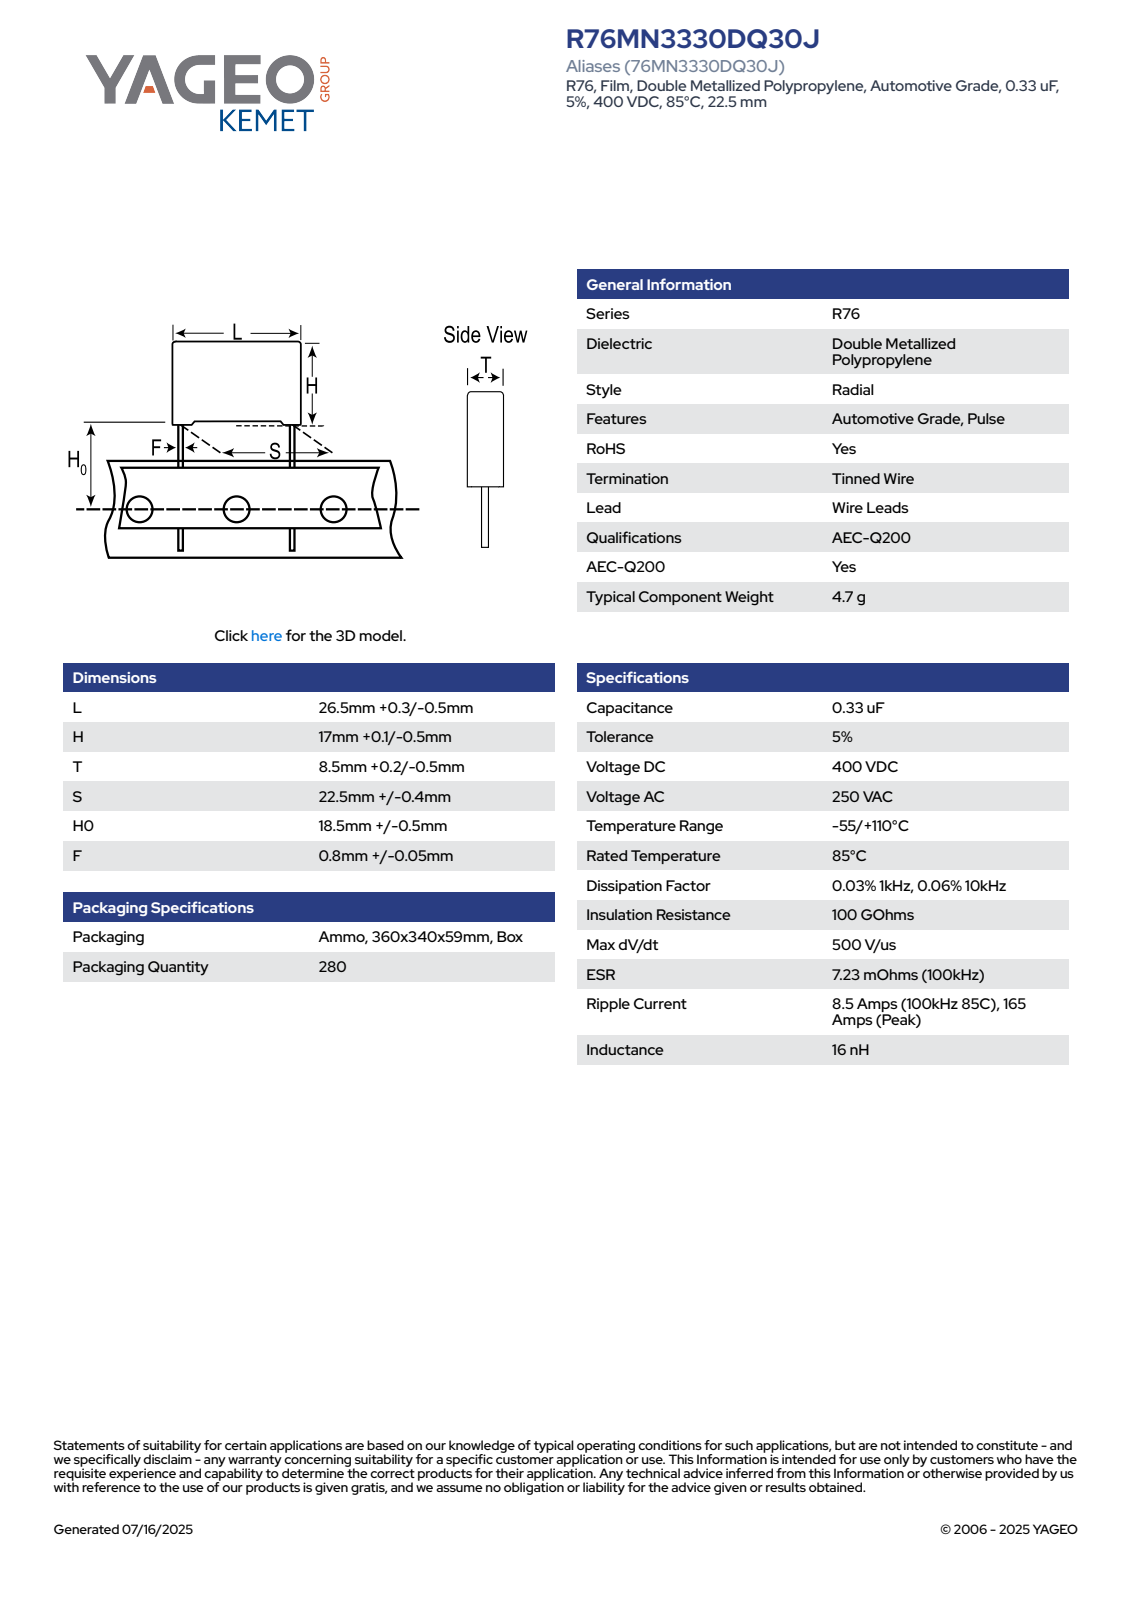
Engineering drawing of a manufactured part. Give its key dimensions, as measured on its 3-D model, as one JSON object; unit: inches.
{"part_name": "CFR_RB2_26.5X17X8.5_L26.8H17.1T8.7S22.5H019F0.85", "step_written_by": "SolidWorks 2020 (AUTOMOTIVE_DESIGN)", "units": "inches", "bodies": {"solids": 4, "faces": 85, "planar": 77, "cylindrical": 8, "other": 0}, "overall_size": [1.421, 1.055, 0.343], "volume_in3": 0.235, "surface_area_in2": 2.835, "round_bosses_or_shafts": [[0.033, 2]], "partial_cylinders_radius": [[0.02, 4]], "face_to_face_distances": [0.343, 0.644, 1.055, 0.65, 0.035, 0.03, 0.023, 0.673, 0.307, 0.343]}
